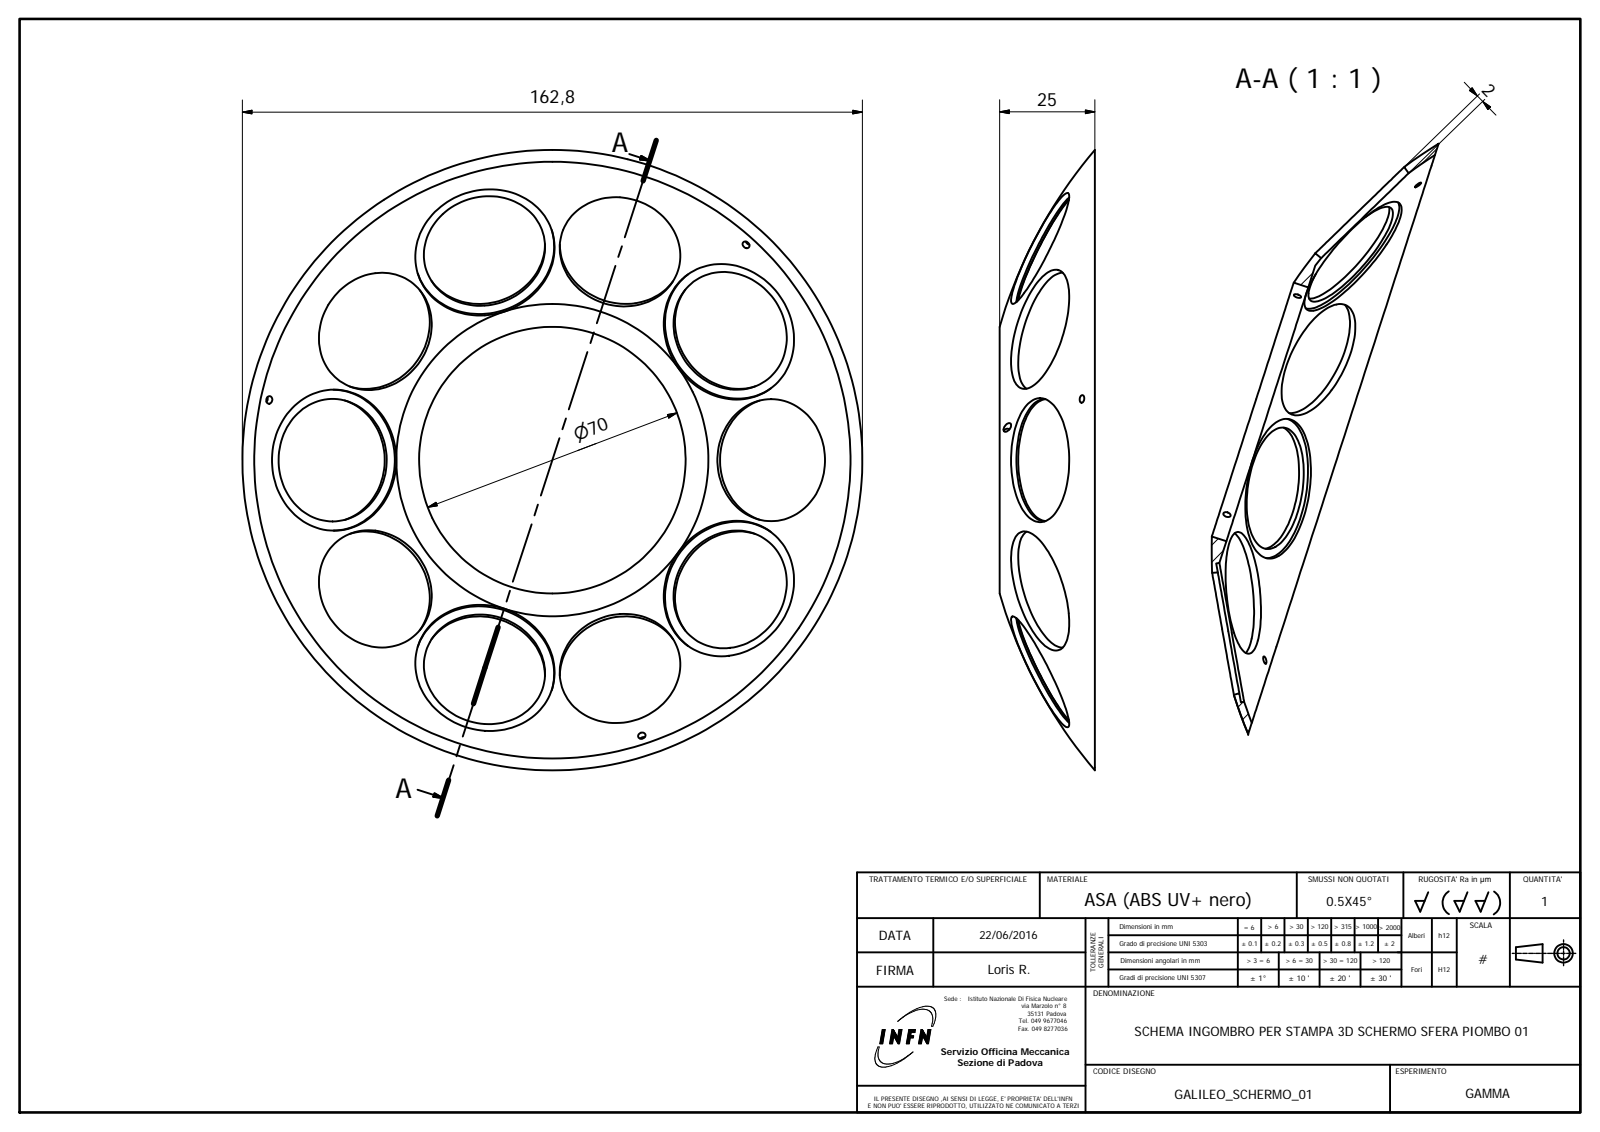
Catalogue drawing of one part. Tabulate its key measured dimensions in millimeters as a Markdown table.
| quantity | value |
| --- | --- |
| part name | mramADF4DA705zcd |
| STEP written by | SIEMENS PLM Software NX 8.5 (AUTOMOTIVE_DESIGN) |
| units | millimeters |
| bodies | 1 solid, 31 faces (7 planar, 12 cylindrical, 12 other) |
| overall size | 335.5 × 251.98 × 170.5 |
| volume | 21 484 mm³ |
| surface area | 25 782 mm² |
| round holes (diameter × count) | 2 × 6, 37 × 5, 70 × 1 |
| main face-to-face distances | 21 |
